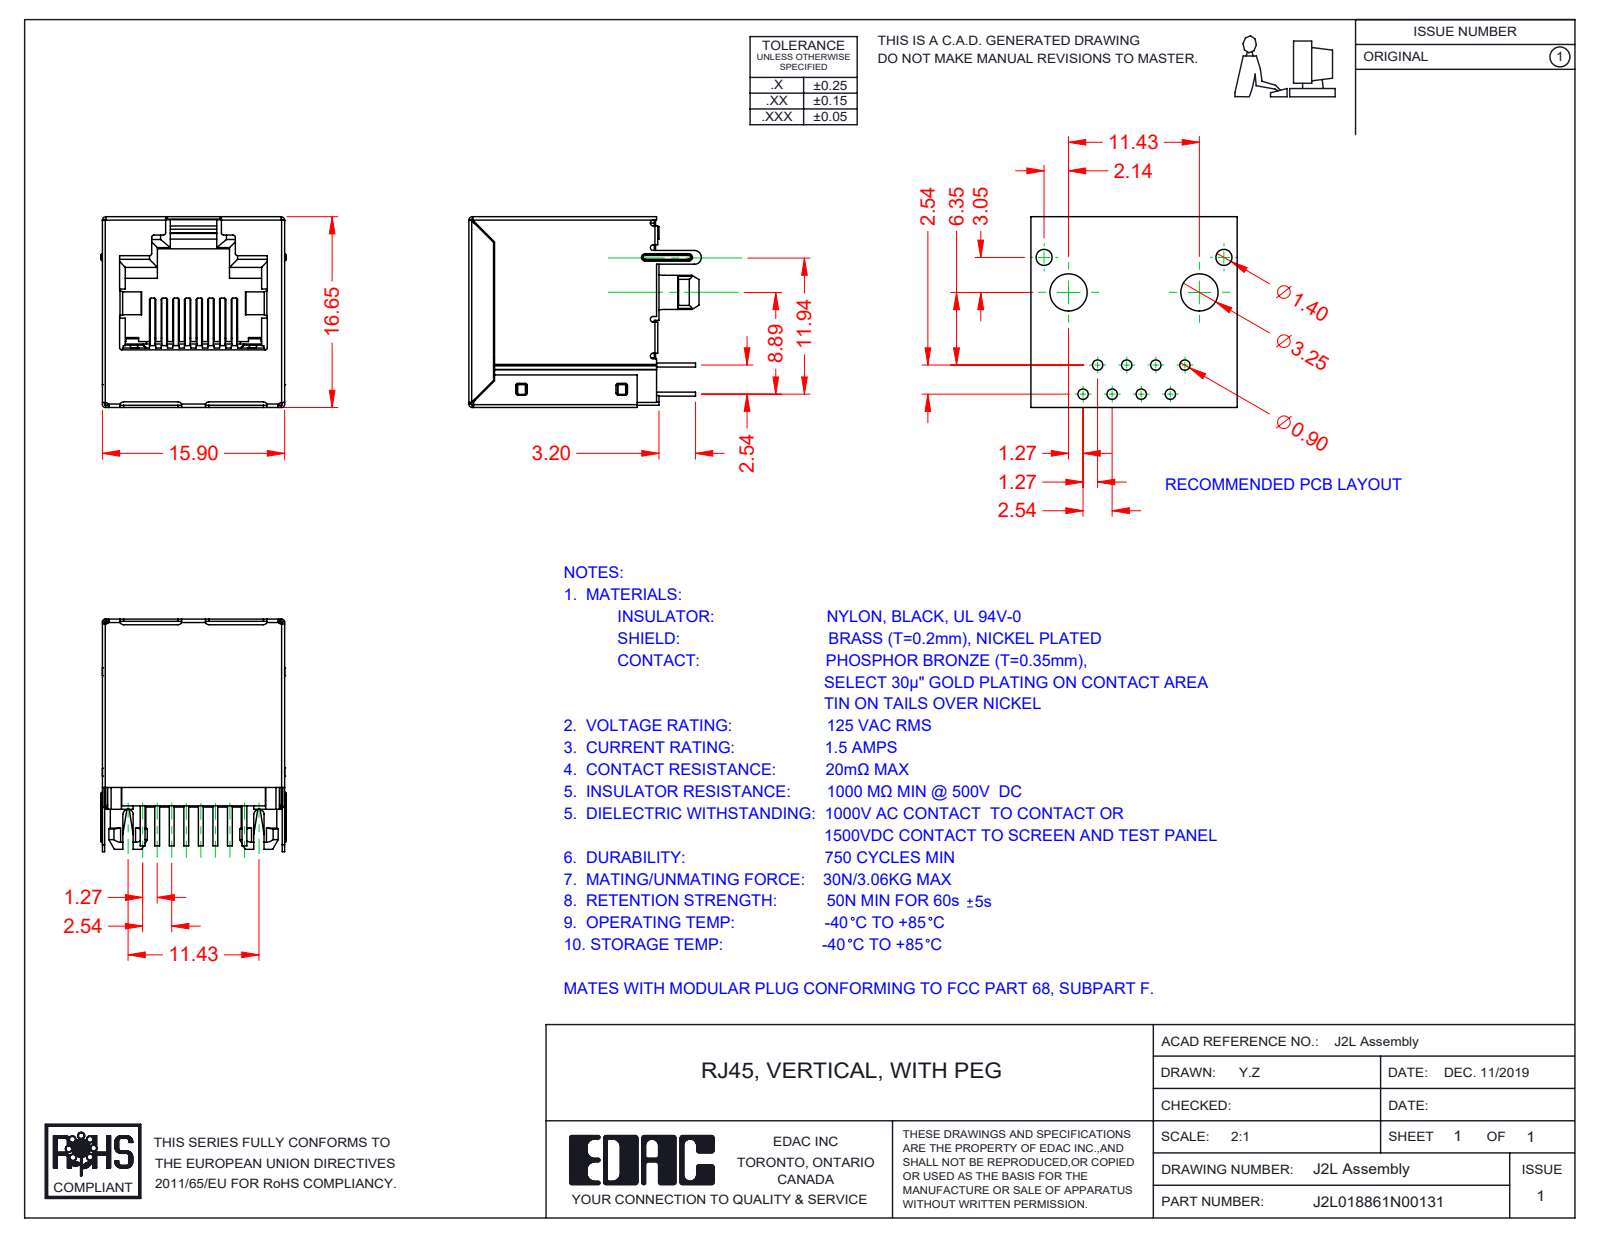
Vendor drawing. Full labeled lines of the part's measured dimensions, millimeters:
Part name (STEP PRODUCT): 2L Contact Lock; 2L Contacts; RJ2L018861N00131; 2L Insulator (+1 more)
STEP written by: SolidWorks 2016 (CONFIG_CONTROL_DESIGN)
Units: millimetres
Bodies: 11 solids, 1125 faces (778 planar, 284 cylindrical, 63 other)
Overall size (bounding box): 20.3 × 16.65 × 16.2
Volume: 2 717 mm³ · Surface area: 6 473 mm²
Round bosses / shafts (diameter × count): ⌀3.1 ×2, ⌀1.1 ×2
Partial cylindrical surfaces — rounded edges, fillets, slot ends (radius × count): R0.15 ×64, R0.25 ×20, R0.2 ×16, R0.3 ×14, R0.35 ×9, R0.1 ×8, R0.28 ×4, R0.5 ×3
Main face-to-face distances: 15.45, 15.7, 16.45, 16.2, 16.4, 15.65, 16.25, 15.9, 15.5, 1.2
